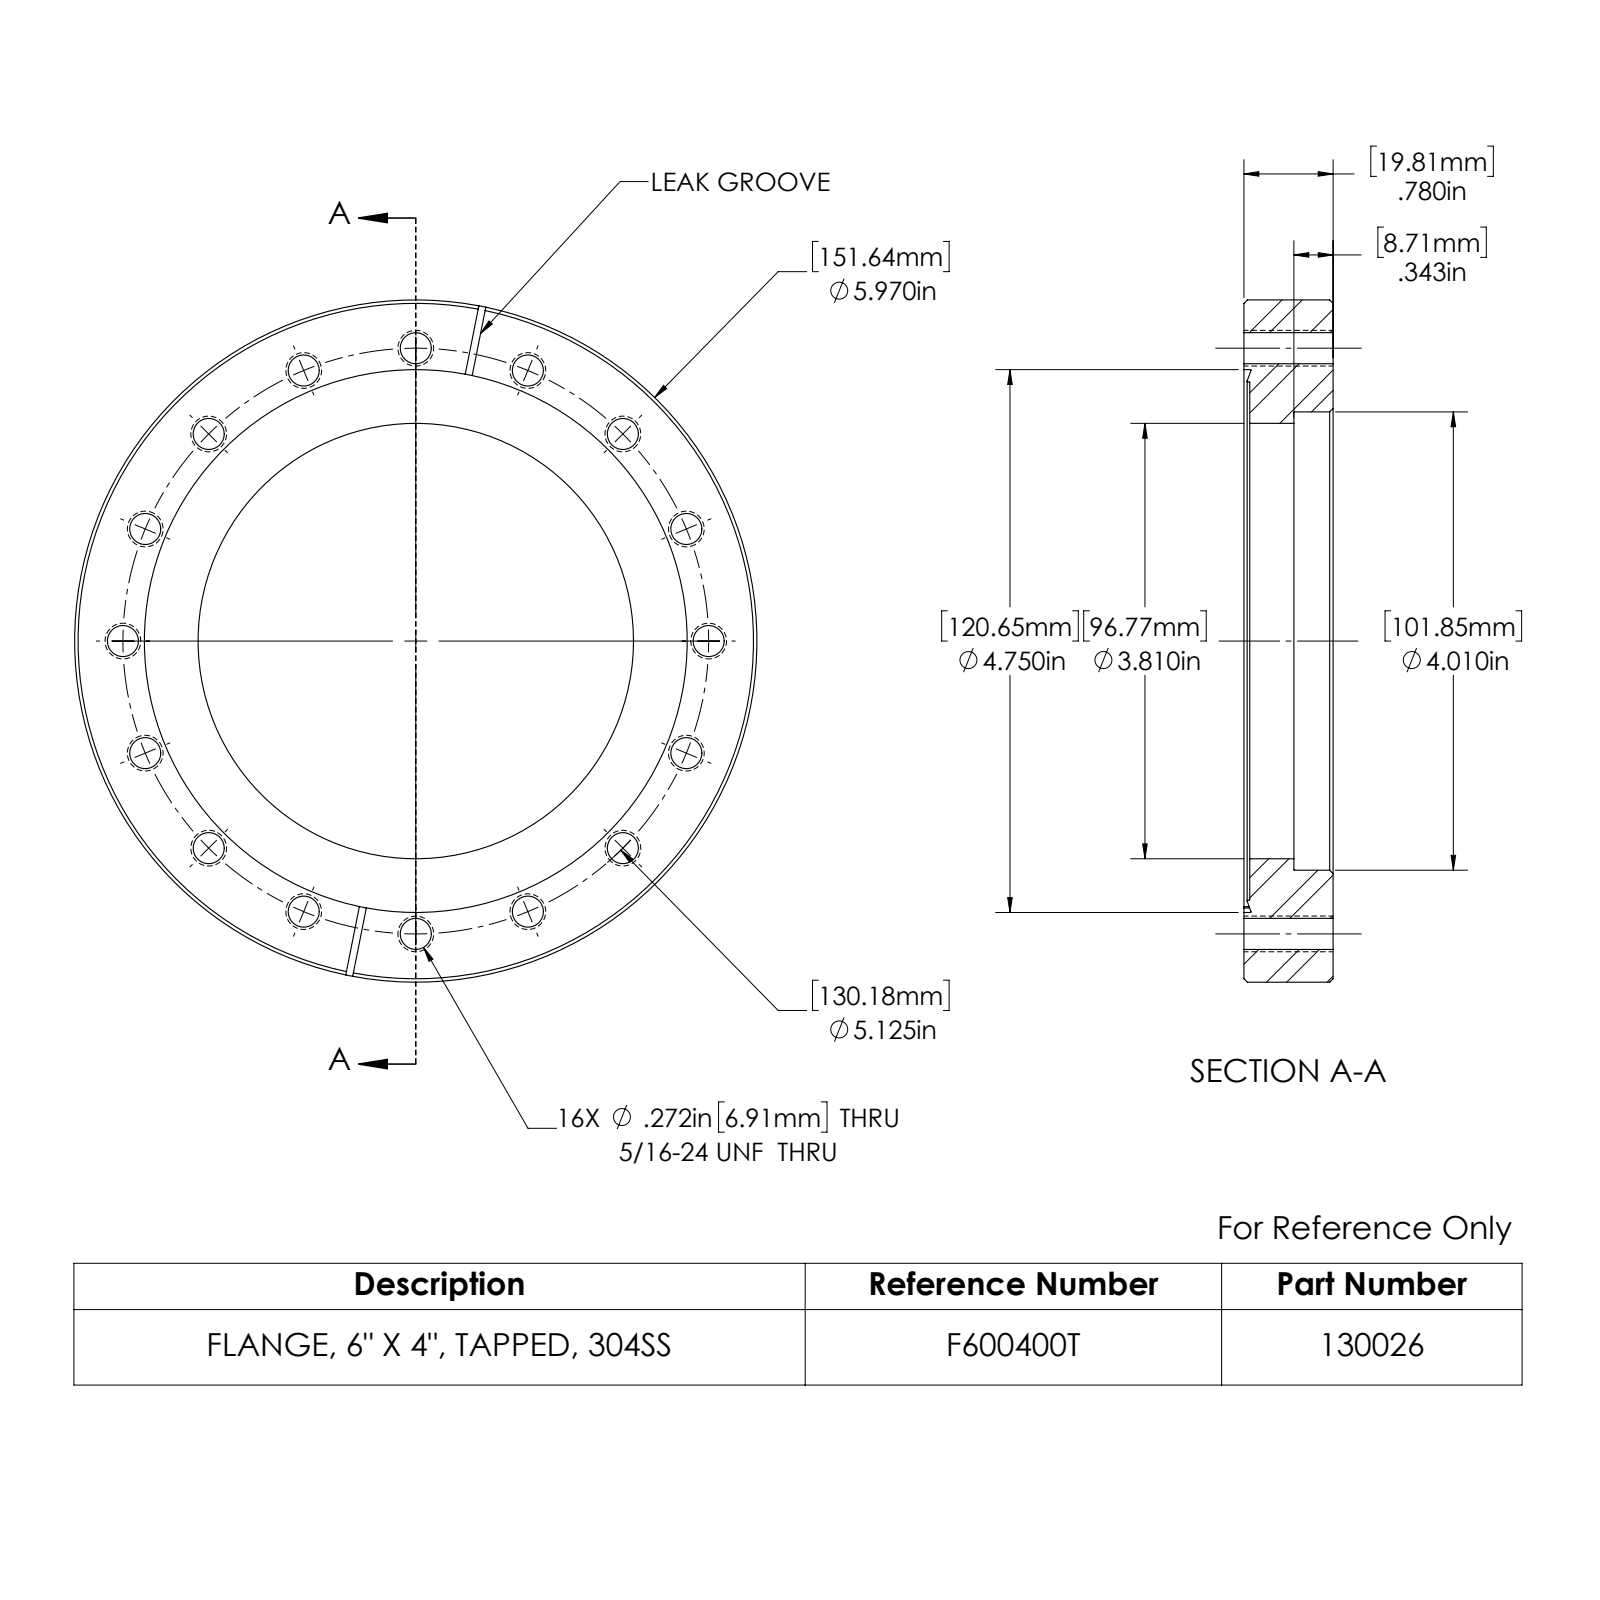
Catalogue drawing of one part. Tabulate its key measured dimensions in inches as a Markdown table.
| quantity | value |
| --- | --- |
| part name | 130026 |
| STEP written by | SolidWorks 2022 (AUTOMOTIVE_DESIGN) |
| units | inches |
| bodies | 1 solid, 70 faces (11 planar, 40 cylindrical, 19 other) |
| overall size | 5.97 × 5.97 × 0.78 |
| volume | 11.46 in³ |
| surface area | 65.98 in² |
| round holes (diameter × count) | 0.272 × 16, 3.81 × 1, 4.01 × 1, 4.75 × 1 |
| round bosses / shafts (diameter × count) | 5.97 × 1 |
| main face-to-face distances | 0.78, 0.051, 0.729, 0.437, 0.386, 0.343, 0.052, 0.385, 0.728, 0.062 |
| hole center spacings | 2.847, 4.735, 5.026, 1.961, 2.563, 3.624, 1, 1 |
